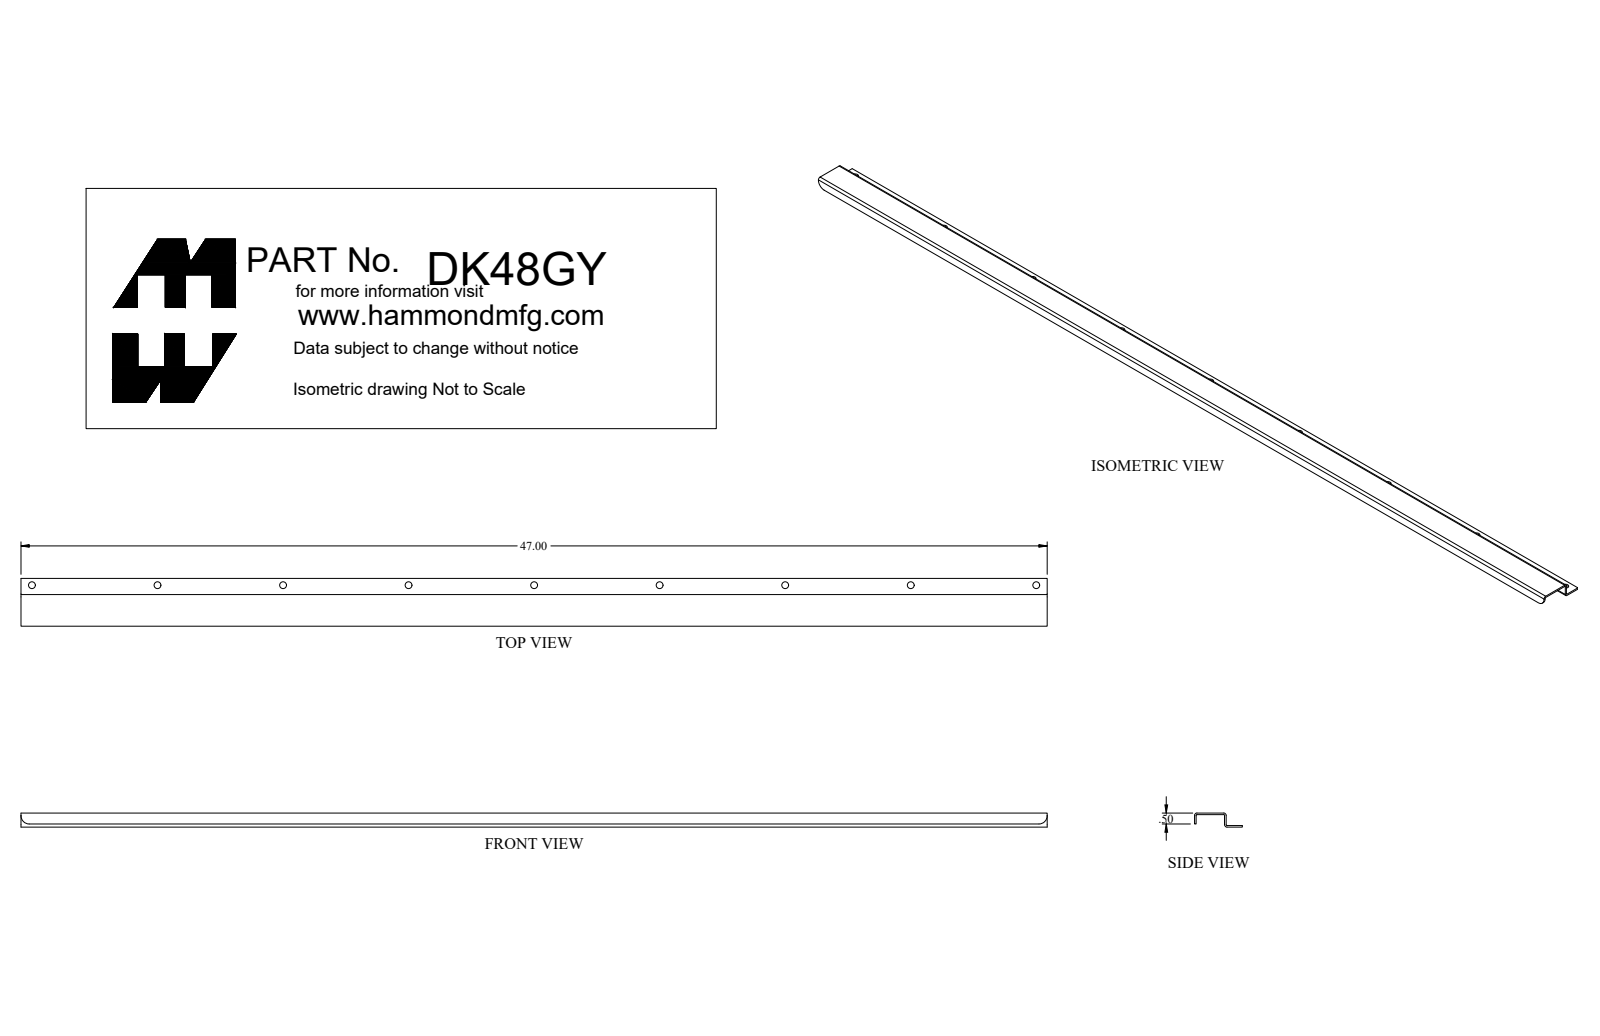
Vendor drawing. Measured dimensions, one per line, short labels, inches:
name: DK48GY_Default
written by: SolidWorks 2018 (CONFIG_CONTROL_DESIGN)
unit: in
bodies: 5 solids, 77 faces (35 planar, 36 cylindrical, 6 other)
size: 47 × 2.188 × 1.322
volume: 12.75 in³; area: 376.5 in²
holes: 9× ⌀0.313, 1× ⌀0.201, 1× ⌀0.275
bosses: 1× ⌀0.625, 1× ⌀0.483, 1× ⌀0.25
rounds: 3× R0.036, 3× R0.108, 2× R0.375
face distances: 0.072, 0.572, 0.644, 1.376, 0.5, 0.063, 0.635, 0.707, 0.135, 1.448
hole spacings: 5.75, 11.5, 17.25, 23, 28.75, 34.5, 40.25, 46
